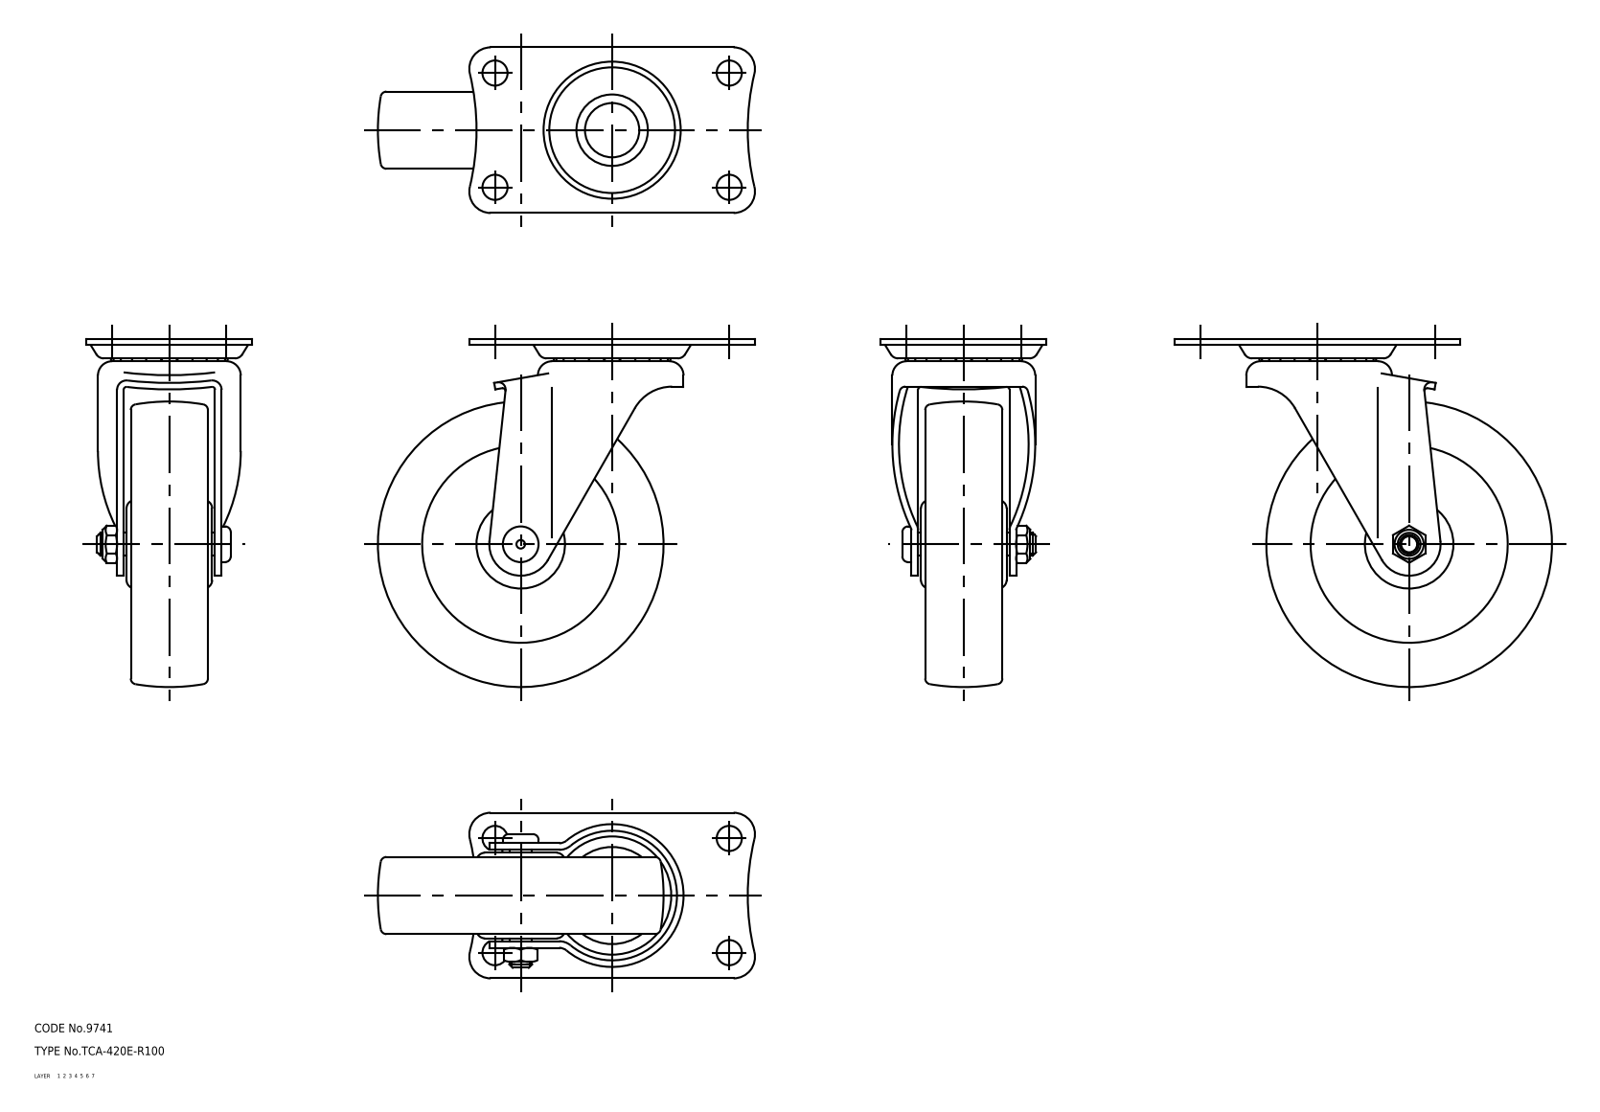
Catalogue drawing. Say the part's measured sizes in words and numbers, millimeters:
The part is named "wheel; mounting plate; main shaft; axle (+1 more)". Its 3-D file was written by "CADfix (AUTOMOTIVE_DESIGN)". It is 5 solids with 224 faces: 0 planar, 0 cylindrical and 224 other. Overall it measures 132 by 122 by 58 millimeters. Its volume is 244 388 cubic millimeters and its surface area 59 138 square millimeters.
